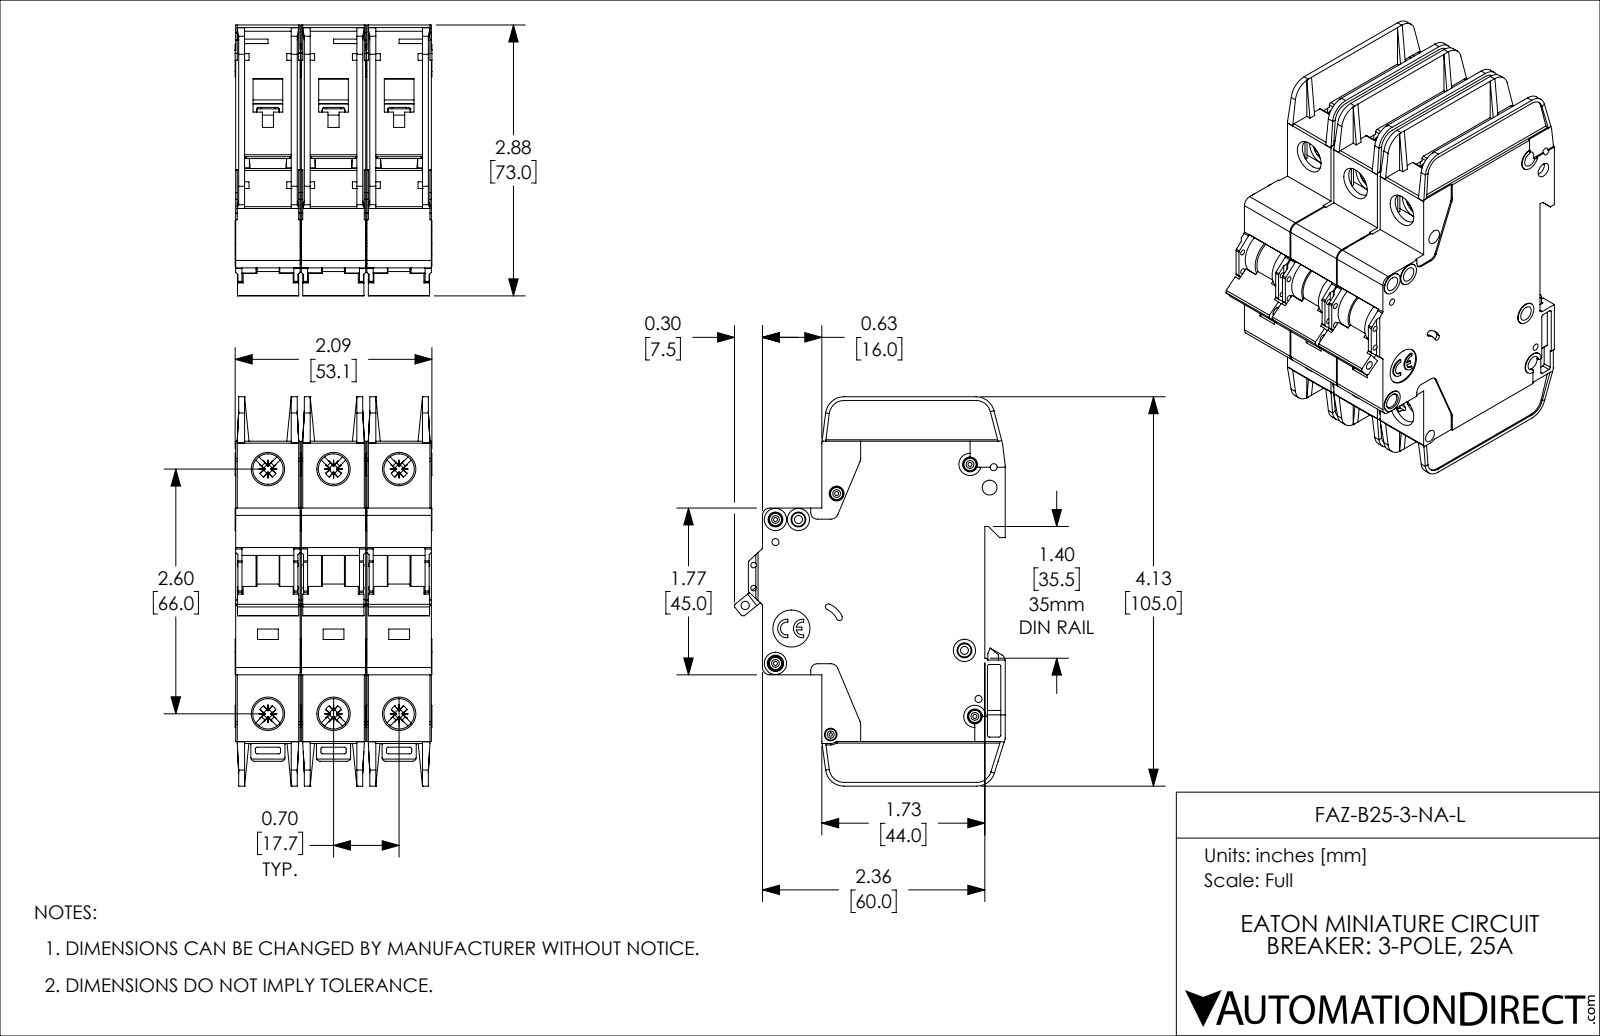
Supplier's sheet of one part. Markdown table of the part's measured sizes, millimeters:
| quantity | value |
| --- | --- |
| part name | FAZ-B25-3-NA-L |
| STEP written by | SolidWorks 2019 (AUTOMOTIVE_DESIGN) |
| units | millimeters |
| bodies | 3 solids, 3381 faces (2013 planar, 1071 cylindrical, 297 other) |
| overall size | 105 × 73.1 × 53.1 |
| volume | 230 200 mm³ |
| surface area | 79 350 mm² |
| round holes (diameter × count) | 4 × 8, 8.2 × 6, 1.1 × 5, 1.9 × 4, 1.5 × 2, 2.2 × 2, 0.9 × 1, 2.3 × 1, 2.5 × 1, 3.4 × 1, 10 × 1 |
| round bosses / shafts (diameter × count) | 3.3 × 5, 6 × 4, 3 × 4, 2.5 × 3 |
| partial cylindrical surfaces (radius × count) | 0.5 × 72, 0.4 × 30, 1 × 18, 1.1 × 12, 2 × 12, 0.2 × 6, 0.3 × 6, 0.7 × 6 |
| main face-to-face distances | 17.7, 1.2, 35.4, 17.4, 15, 35.1, 18.9, 16.5, 2.7, 2.4 |
| hole center spacings | 17.7, 68.3, 66, 6.2, 13.6, 22.1, 35.4, 74.9 |
